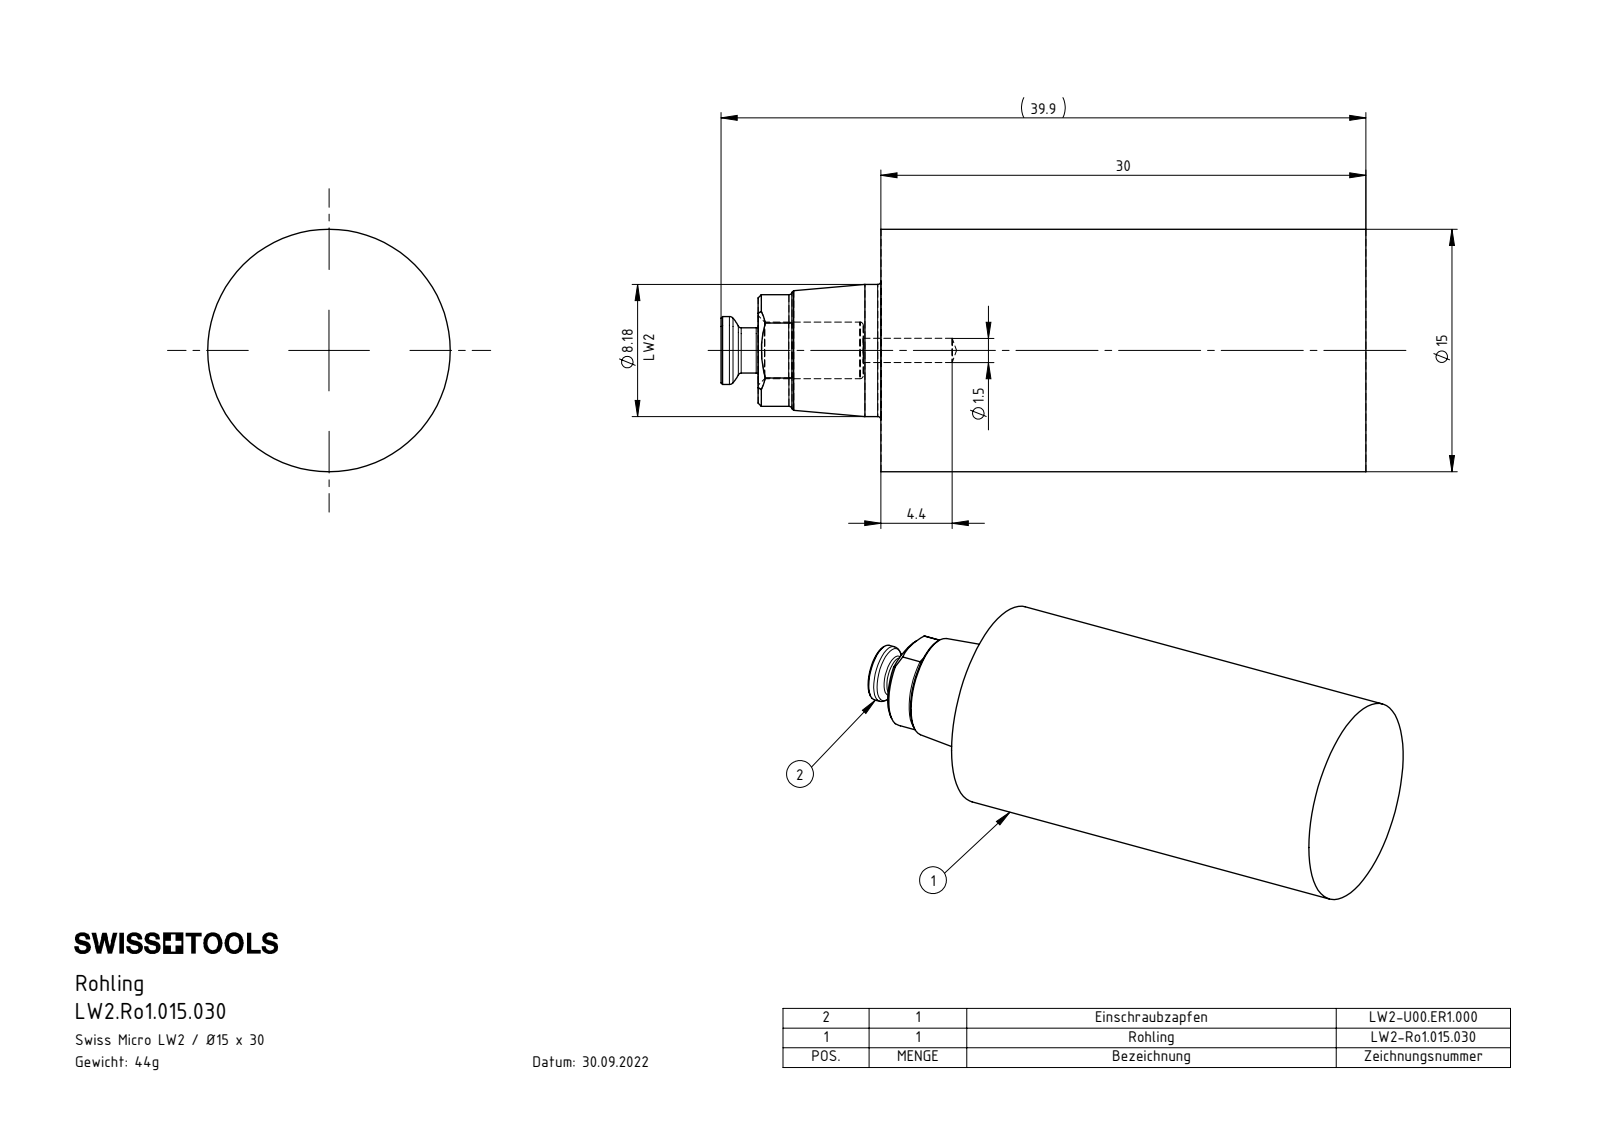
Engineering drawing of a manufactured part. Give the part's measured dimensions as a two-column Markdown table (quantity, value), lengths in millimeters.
| quantity | value |
| --- | --- |
| part name | LW2-U00.ER1.000_A; LW2.Ro1.015.030; LW2-Ro1.015.030_A |
| STEP written by | SolidWorks 2017 (AUTOMOTIVE_DESIGN) |
| units | millimeters |
| bodies | 2 solids, 92 faces (10 planar, 38 cylindrical, 44 other) |
| overall size | 39.9 × 15 × 15 |
| volume | 5 644 mm³ |
| surface area | 2 176 mm² |
| round holes (diameter × count) | 1 × 1, 1.5 × 1, 3.5 × 1 |
| round bosses / shafts (diameter × count) | 15 × 1, 8.18 × 1, 4.2 × 1, 4 × 1, 3 × 1, 2.8 × 1 |
| partial cylindrical surfaces (radius × count) | 0.19 × 6, 0.29 × 6, 0.2 × 2, 3.45 × 1 |
| main face-to-face distances | 30, 7.6, 37.6, 6.5, 1.1, 31.1, 2.3, 8.8, 9.9, 39.9 |
